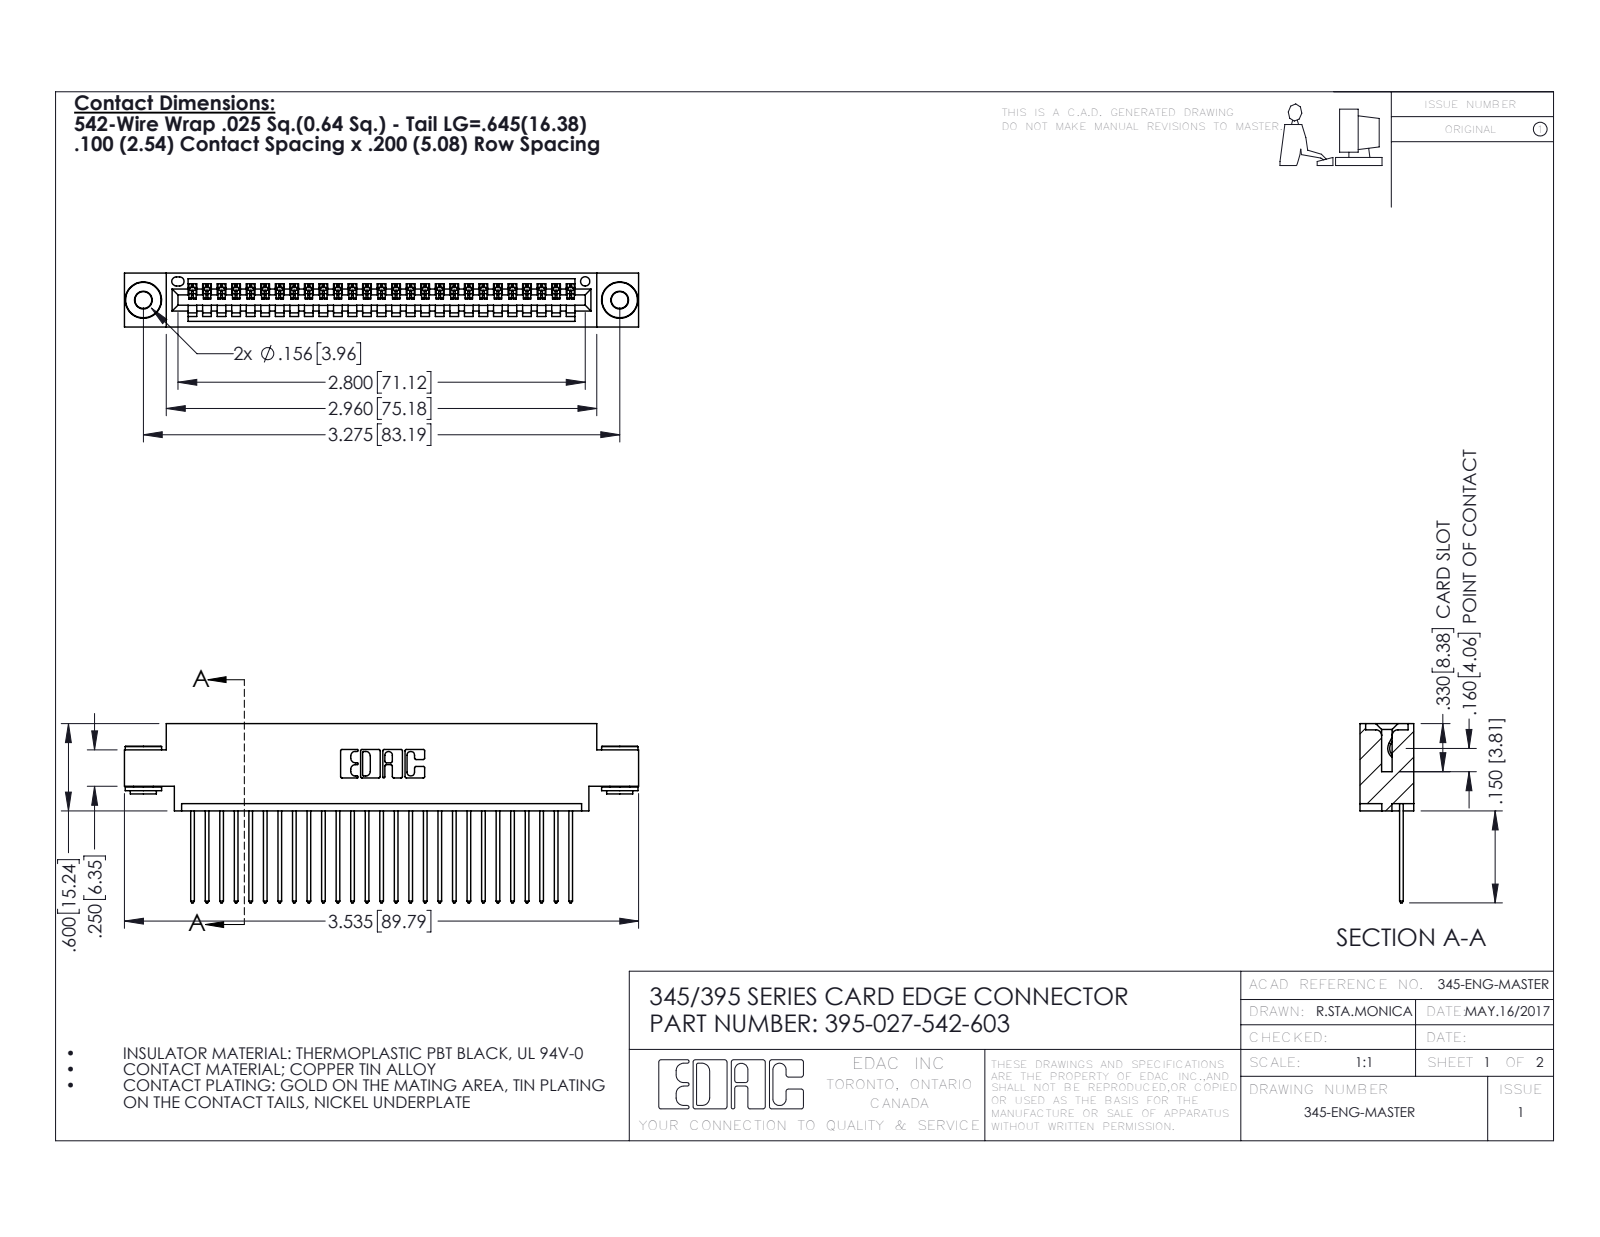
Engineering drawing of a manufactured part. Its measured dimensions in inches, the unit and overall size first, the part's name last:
Units: inches
Overall size (bounding box): 3.535 × 1.232 × 0.37
Round holes (diameter × count): ⌀0.116 ×2, ⌀0.156 ×2, ⌀0.064 ×1
Round bosses / shafts (diameter × count): ⌀0.25 ×2, ⌀0.18 ×2, ⌀0.136 ×2
Partial cylindrical surfaces — rounded edges, fillets, slot ends (radius × count): R0.006 ×54, R0.01 ×54, R0.01 ×22, R0.007 ×6, R0.031 ×6, R0.026 ×3, R0.031 ×2, R0.04 ×2
Main face-to-face distances: 0.072, 0.298, 0.37, 0.098, 0.272, 0.025, 0.2, 0.225, 0.175, 0.1
Hole centre spacings: 0.27, 3.04, 3.275
Volume: 0.511 in³ · Surface area: 18.05 in²
Bodies: 30 solids, 1734 faces (1174 planar, 552 cylindrical, 8 other)
Part name (STEP PRODUCT): 345 Part_0.170 Offset - 0.156 Dia-TH; 345-250-002_345-250-002-102; 395-027-542-603; 345-292-001_345-293-142
STEP written by: SolidWorks 2016 (CONFIG_CONTROL_DESIGN)
